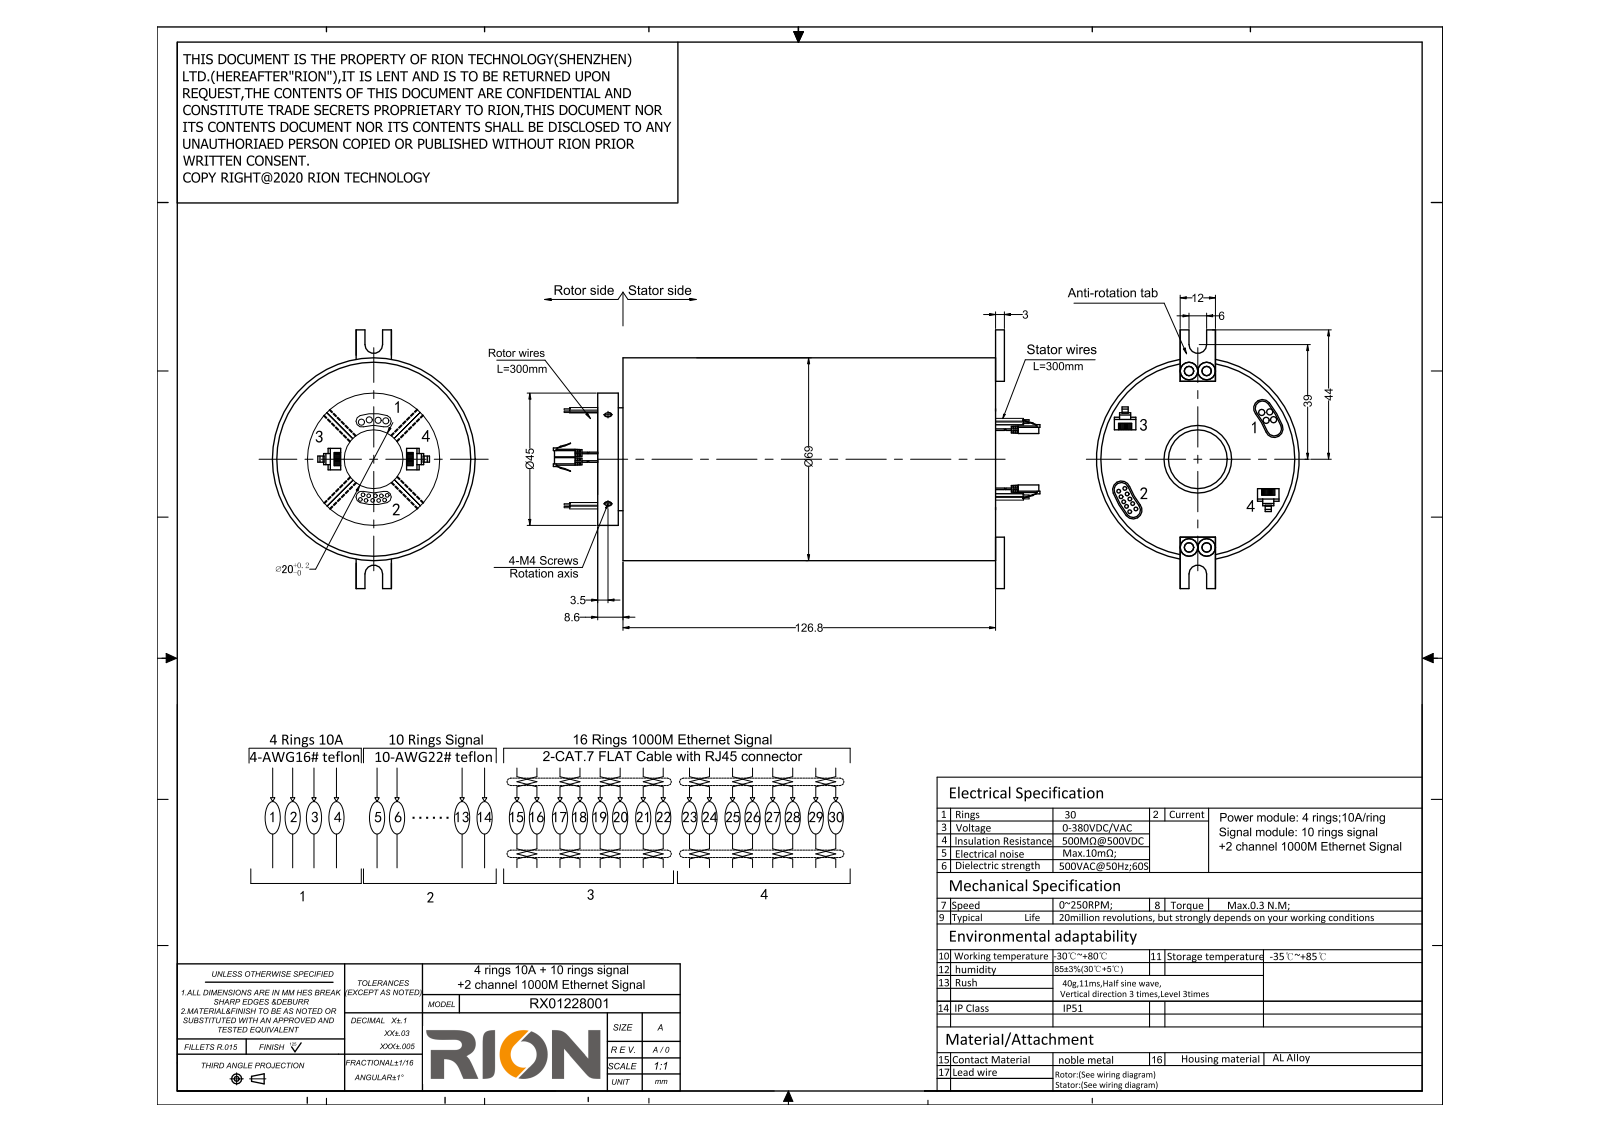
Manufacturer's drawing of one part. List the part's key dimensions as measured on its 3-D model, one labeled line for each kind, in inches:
Part name (STEP PRODUCT): ME2202-P0410-S10(Z1567)
STEP written by: SolidWorks 2014 (CONFIG_CONTROL_DESIGN)
Units: inches
Bodies: 1 solid, 251 faces (99 planar, 136 cylindrical, 16 other)
Overall size (bounding box): 7.22 × 3.465 × 2.717
Volume: 27.23 in³ · Surface area: 87.15 in²
Round holes (diameter × count): ⌀0.098 ×4, ⌀0.126 ×4, ⌀0.13 ×2, ⌀0.787 ×1, ⌀0.913 ×1, ⌀2.598 ×1
Round bosses / shafts (diameter × count): ⌀0.051 ×20, ⌀0.083 ×8, ⌀2.717 ×1, ⌀2.591 ×1, ⌀1.772 ×1, ⌀1.378 ×1, ⌀0.906 ×1
Partial cylindrical surfaces — rounded edges, fillets, slot ends (radius × count): R0.079 ×16, R0.118 ×2, R0.61 ×1
Main face-to-face distances: 4.992, 5.331, 0.339, 5.055, 0.063, 0.276, 0.055, 0.118, 0.236, 1.016
Hole centre spacings: 1.187, 0.236, 2.362, 2.374
